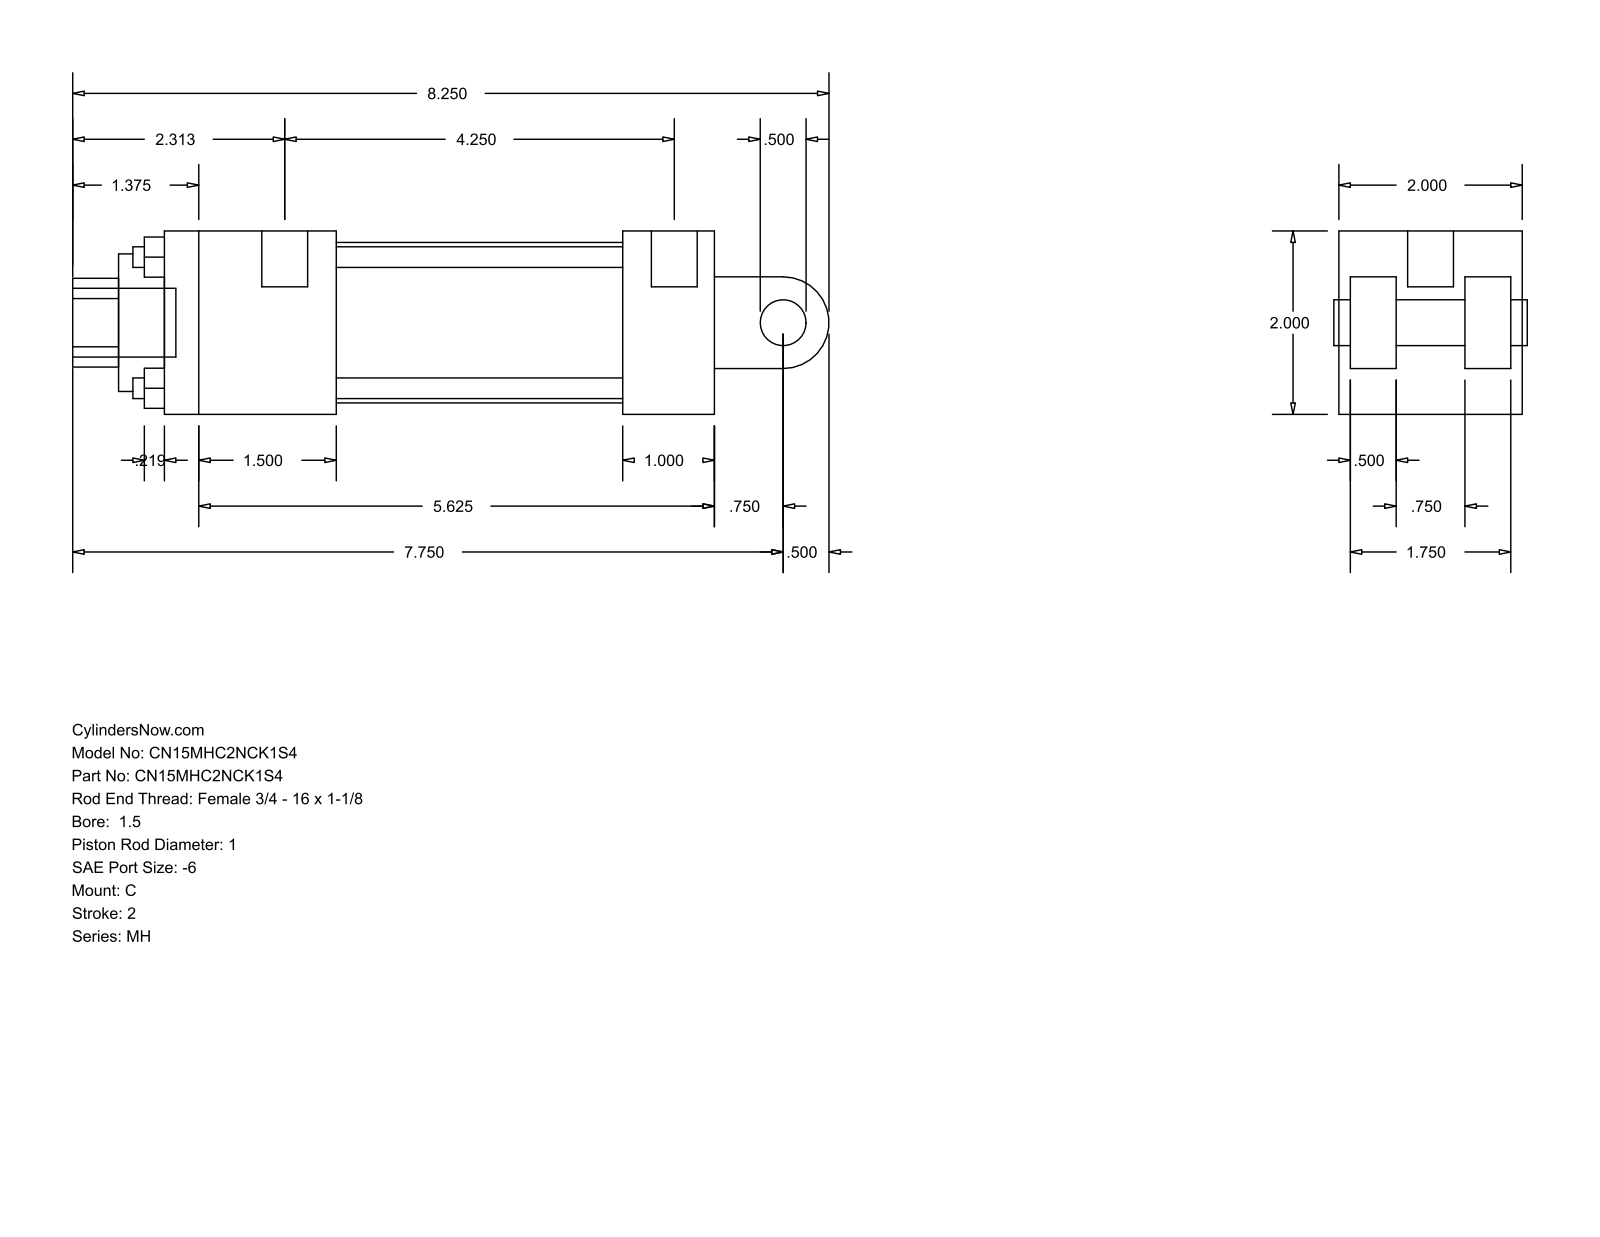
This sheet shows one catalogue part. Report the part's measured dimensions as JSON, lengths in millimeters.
{"part_name": "MH_C__0150_1", "step_written_by": "GSSL Pune (CONFIG_CONTROL_DESIGN)", "units": "millimeters", "bodies": {"solids": 0, "faces": 99, "planar": 70, "cylindrical": 29, "other": 0}, "overall_size": [209.55, 50.8, 50.8], "round_holes": [[5.71, 4], [5.56, 2], [12.7, 1], [25.4, 1], [38.1, 1], [44.45, 1]], "round_bosses_or_shafts": [[12.7, 2], [5.56, 2], [19.05, 1]], "partial_cylinders_radius": [[12.29, 1], [12.7, 1]], "face_to_face_distances": [50.8, 12.7, 47.63, 3.17, 15.87, 25.4, 34.93, 31.76, 152.4, 38.1], "hole_center_spacings": [25.68, 36.32, 51.36]}
